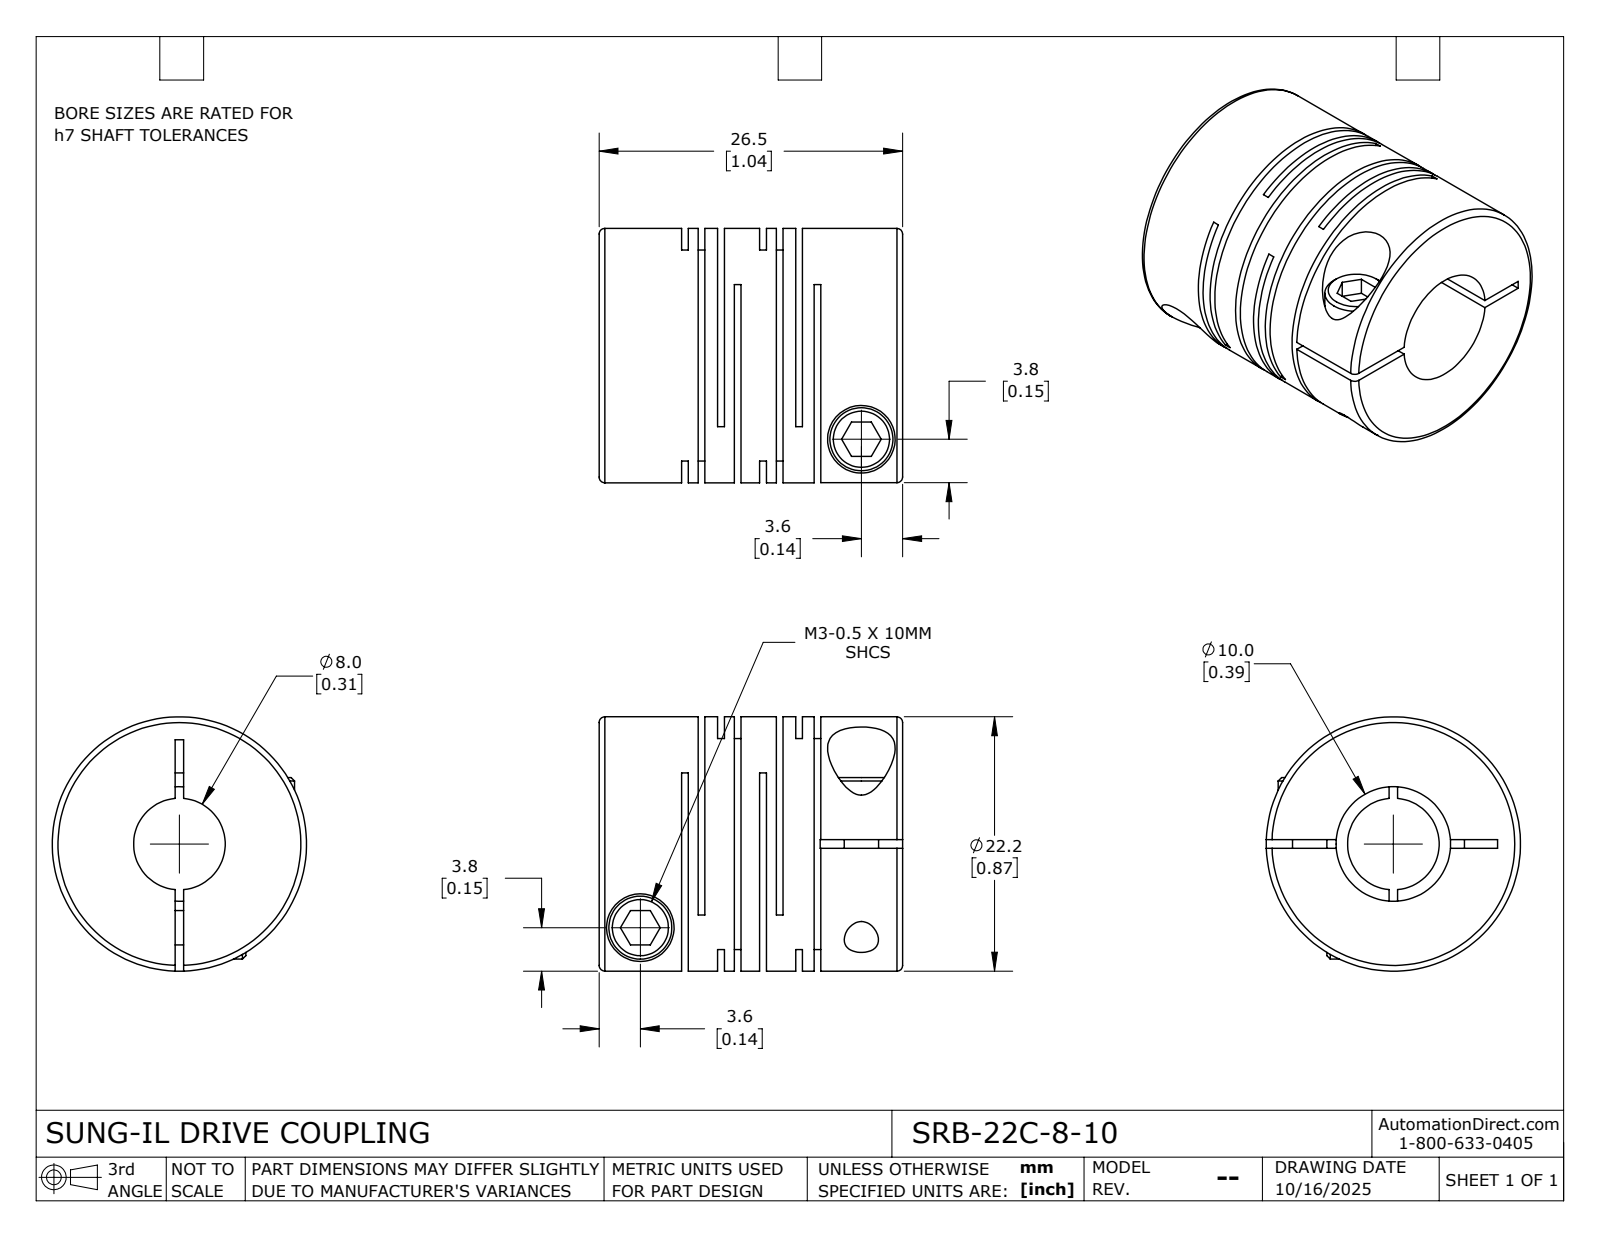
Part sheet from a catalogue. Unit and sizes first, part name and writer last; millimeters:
Units: millimetres
Overall size (bounding box): 26.5 × 22.2 × 22.2
Round holes (diameter × count): ⌀3 ×2, ⌀5.9 ×2, ⌀8 ×1, ⌀10 ×1
Round bosses / shafts (diameter × count): ⌀5.5 ×2, ⌀22.2 ×1
Main face-to-face distances: 0.59, 3.15, 6.82, 1.45, 5.37, 3.67, 1.7, 2.04, 3.74, 7.41
Volume: 6 915 mm³ · Surface area: 7 454 mm²
Bodies: 1 solid, 115 faces (60 planar, 42 cylindrical, 13 other)
Part name (STEP PRODUCT): SRB-22C-8-10
STEP written by: SolidWorks 2024 (CONFIG_CONTROL_DESIGN)
